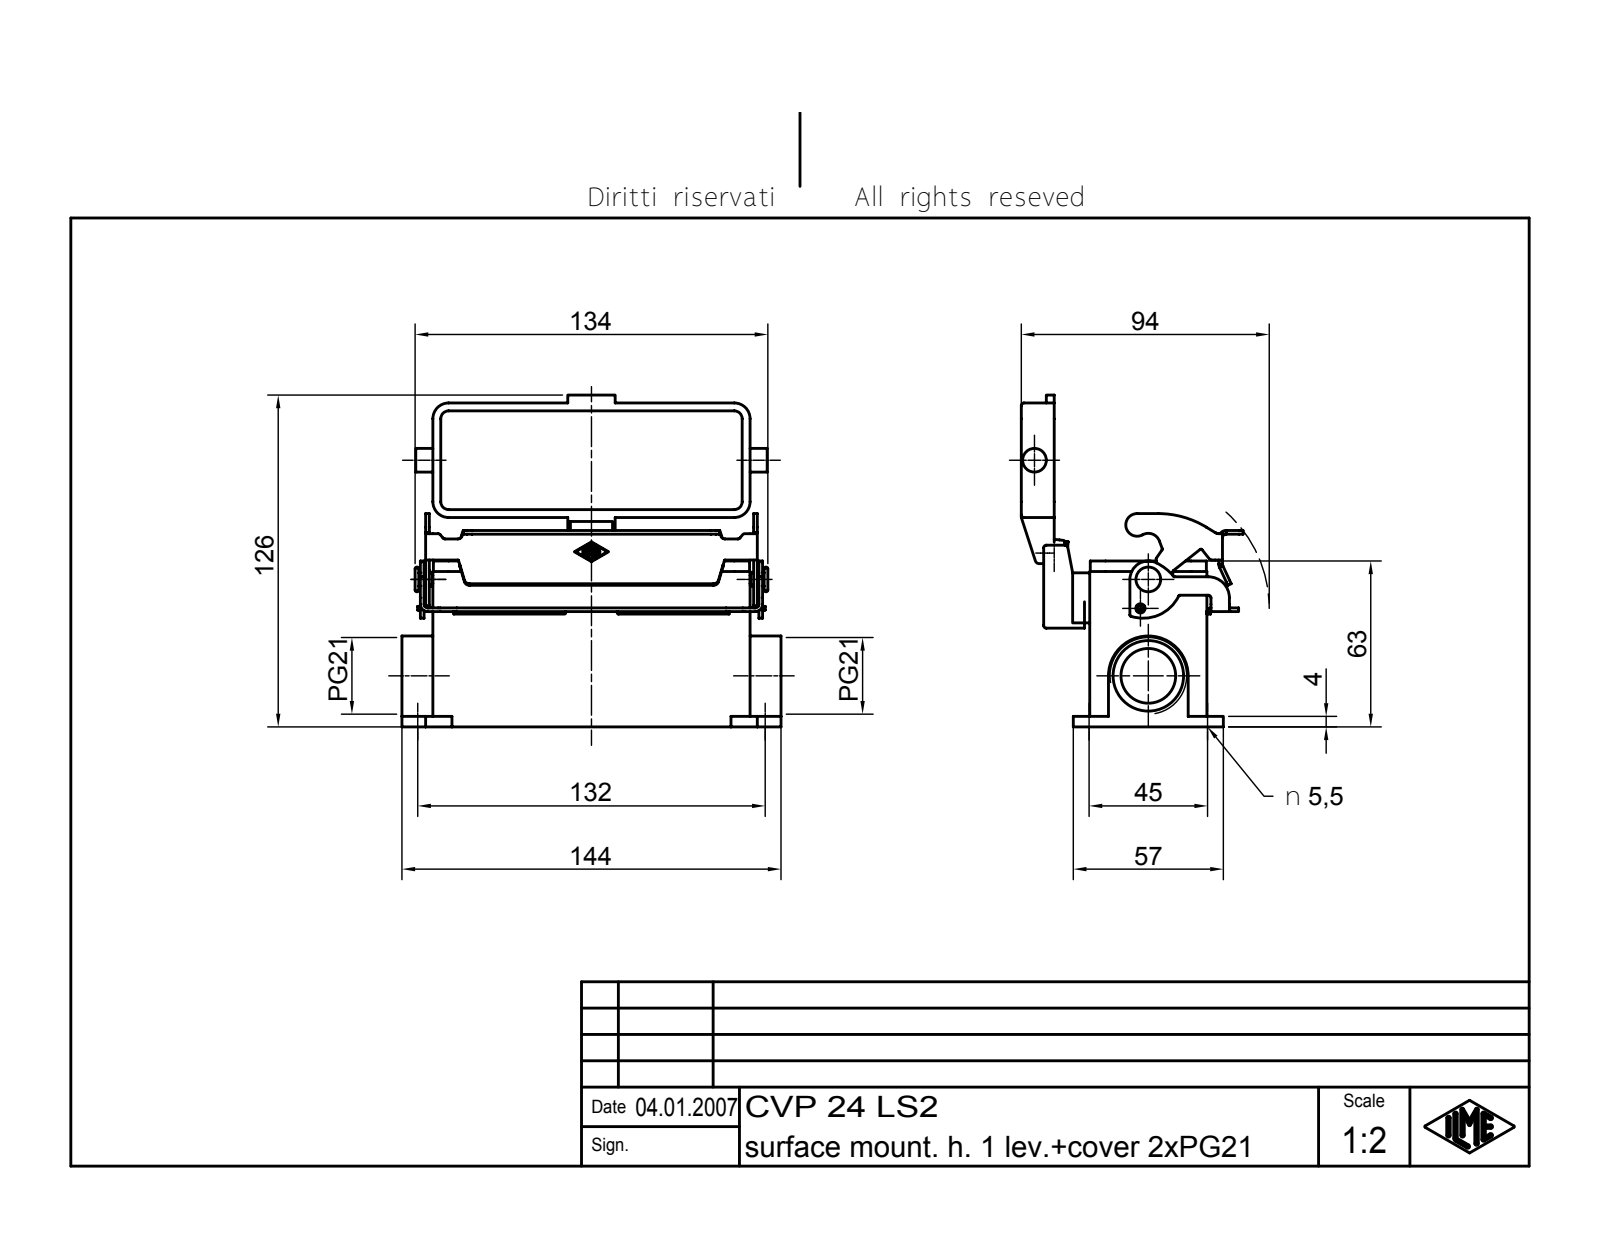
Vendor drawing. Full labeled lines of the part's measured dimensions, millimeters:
Part name (STEP PRODUCT): CVP 24 LS2
STEP written by: Autodesk Inventor 7 (AUTOMOTIVE_DESIGN)
Units: millimetres
Bodies: 4 solids, 572 faces (222 planar, 185 cylindrical, 165 other)
Overall size (bounding box): 144 × 126 × 84.23
Volume: 159 413 mm³ · Surface area: 93 334 mm²
Round holes (diameter × count): ⌀5.5 ×4, ⌀3.5 ×1, ⌀4 ×1, ⌀20.78 ×1, ⌀26.78 ×1
Round bosses / shafts (diameter × count): ⌀5 ×2, ⌀9 ×1, ⌀7 ×1, ⌀3.2 ×1, ⌀3 ×1
Partial cylindrical surfaces — rounded edges, fillets, slot ends (radius × count): R1 ×27, R0.25 ×15, R0.5 ×10, R1.5 ×10, R6 ×8, R2 ×7, R1.4 ×6, R2.8 ×6
Main face-to-face distances: 4, 40.5, 44.5, 36.5, 30, 23.5, 70.5, 66.5, 26, 2.5
Hole centre spacings: 45, 132, 139.46, 25.79
